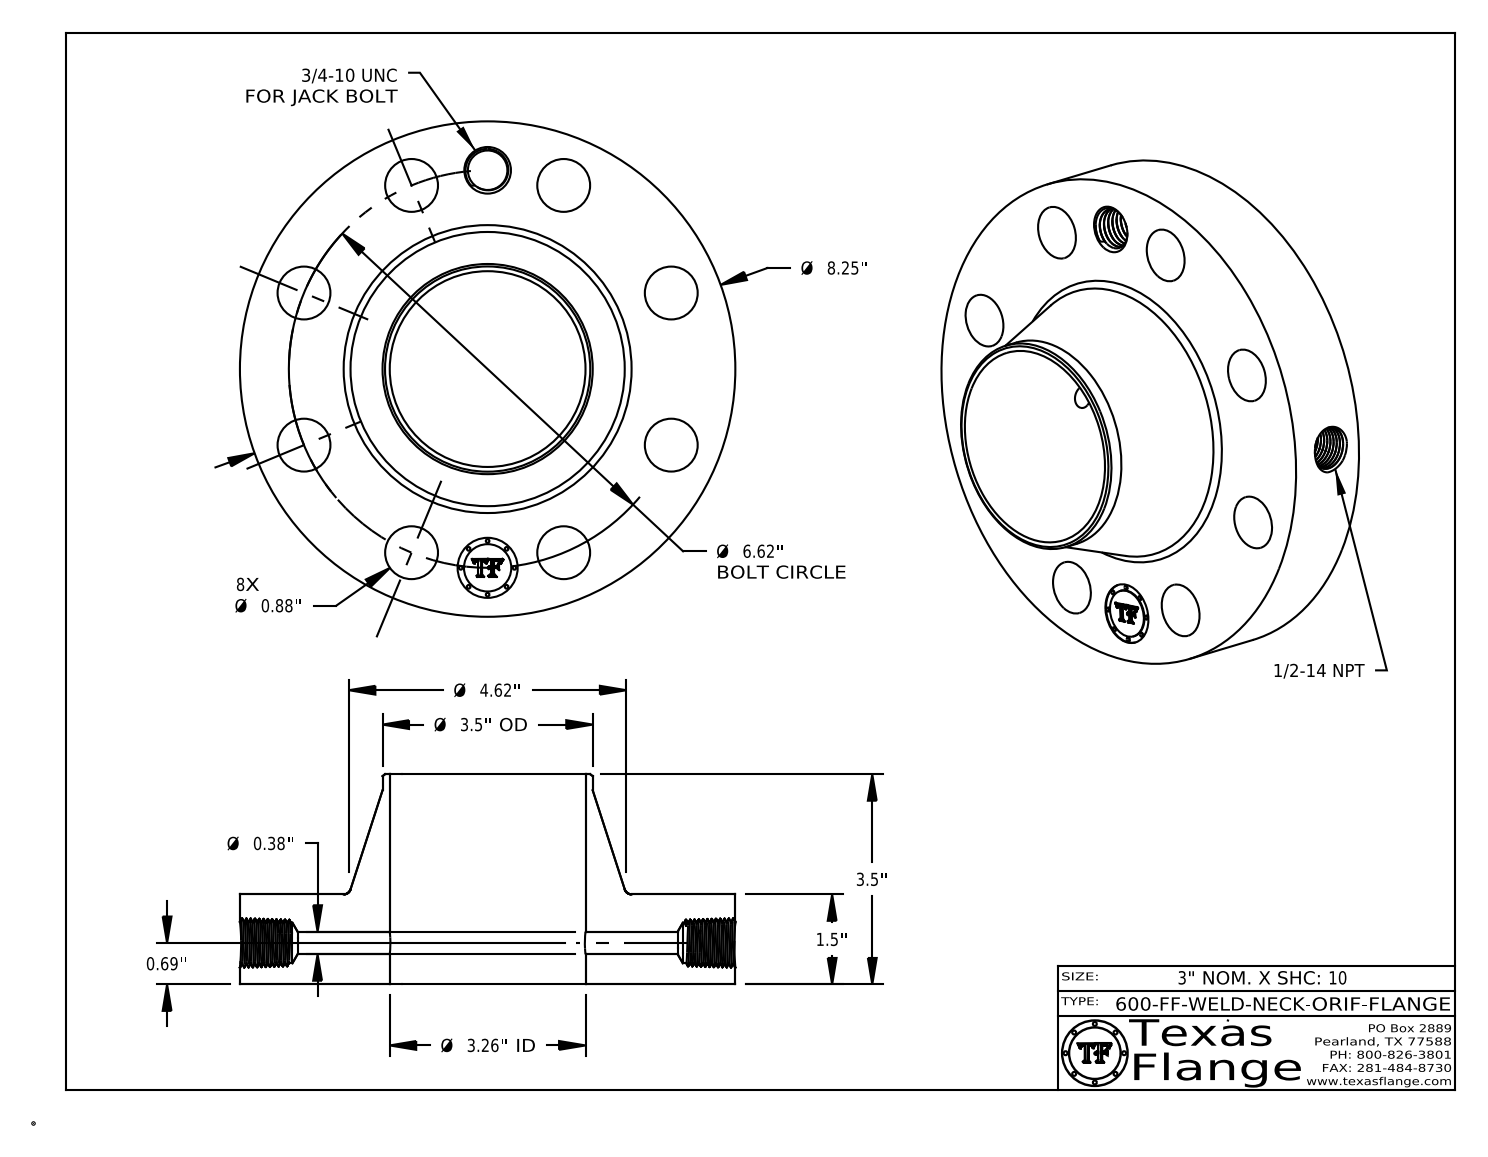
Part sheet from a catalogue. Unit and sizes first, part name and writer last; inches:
Units: inches
Overall size (bounding box): 8.25 × 8.25 × 3.5
Round holes (diameter × count): ⌀0.88 ×8, ⌀0.375 ×1, ⌀0.656 ×1, ⌀0.672 ×1, ⌀1 ×1, ⌀3.26 ×1
Round bosses / shafts (diameter × count): ⌀0.061 ×8, ⌀8.25 ×1, ⌀3.5 ×1, ⌀0.788 ×1
Main face-to-face distances: 1.5, 3.5, 2, 0.015, 1.485, 2.015, 0.298, 0.293, 0.054, 0.248
Hole centre spacings: 3.31, 4.681, 6.116, 6.62, 1.291, 2.533, 2.533, 3.678
Volume: 67.12 in³ · Surface area: 220.9 in²
Bodies: 1 solid, 766 faces (368 planar, 90 cylindrical, 308 other)
Part name (STEP PRODUCT): 600-FF-WELD-NECK
STEP written by: CATIA V5 STEP AP214 (AUTOMOTIVE_DESIGN)
